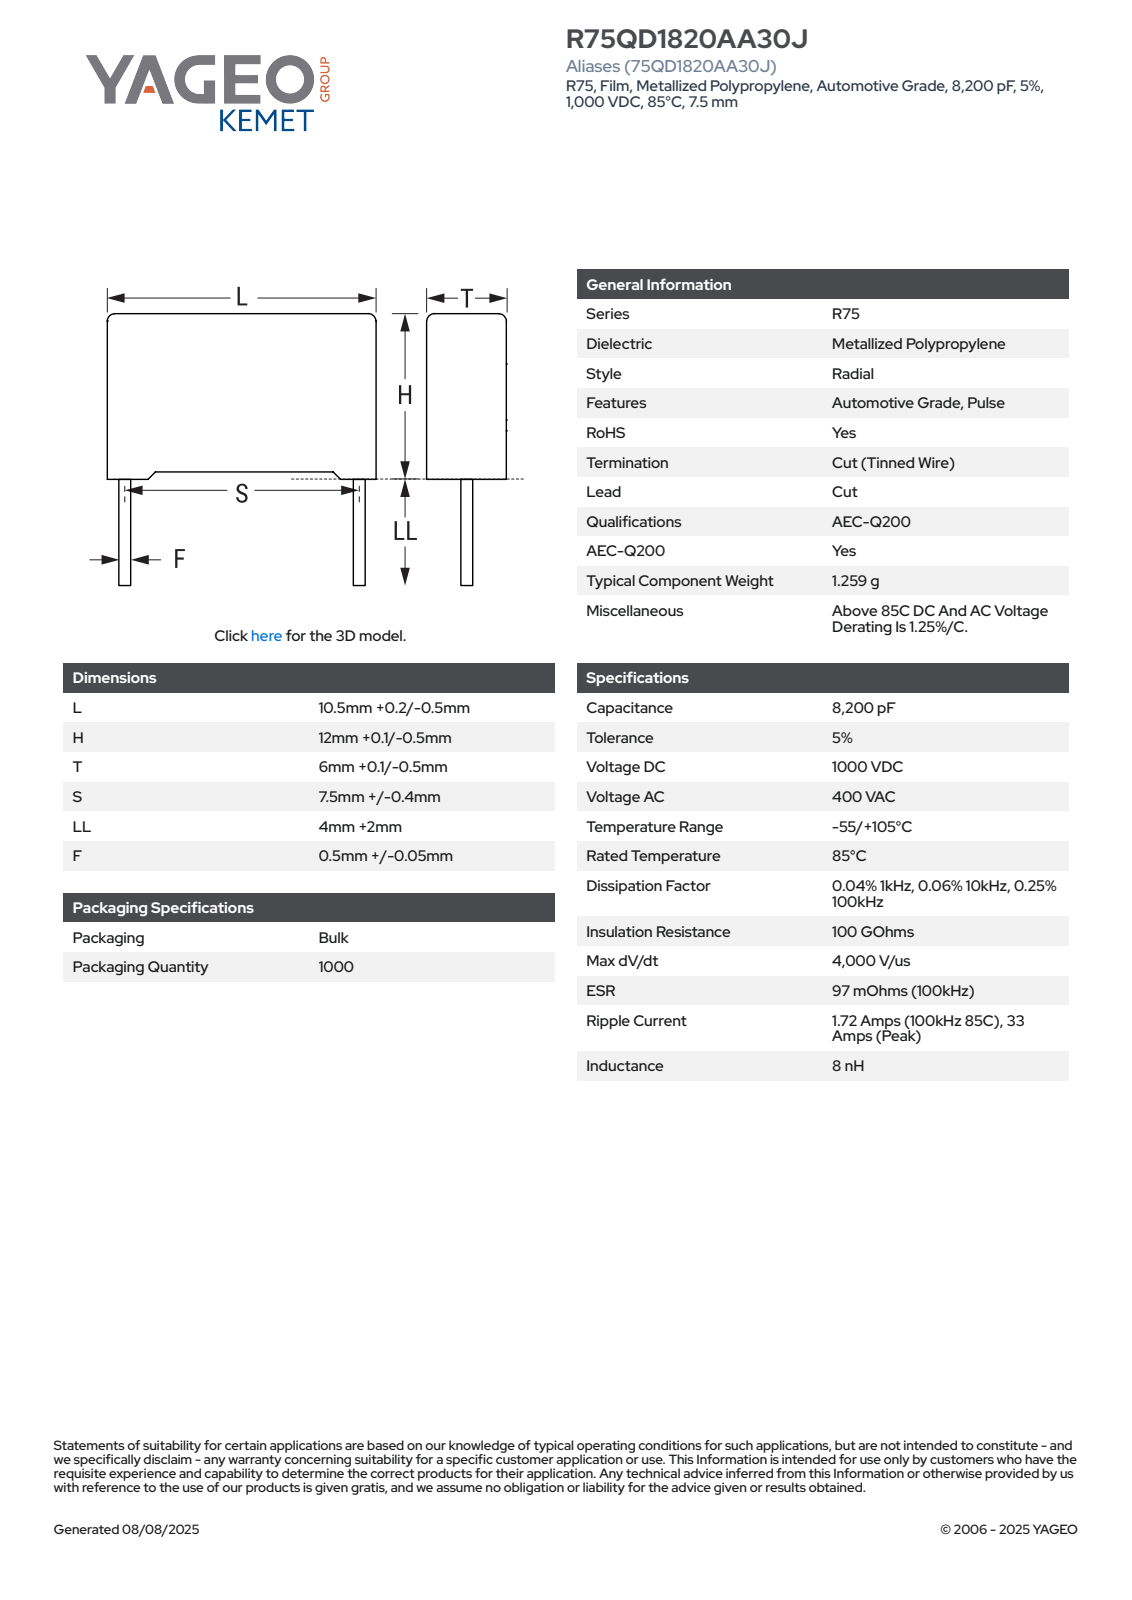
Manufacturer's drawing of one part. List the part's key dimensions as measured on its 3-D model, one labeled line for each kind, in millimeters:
Part name (STEP PRODUCT): CFR_RB2_10.5X12X6_L10.7H12.1T6.1S7.5LL6F0.55
STEP written by: SolidWorks 2021 (AUTOMOTIVE_DESIGN)
Units: millimetres
Bodies: 4 solids, 85 faces (77 planar, 8 cylindrical, 0 other)
Overall size (bounding box): 18.1 × 10.7 × 6.11
Volume: 750 mm³ · Surface area: 578 mm²
Round bosses / shafts (diameter × count): ⌀0.55 ×2
Partial cylindrical surfaces — rounded edges, fillets, slot ends (radius × count): R0.5 ×4
Main face-to-face distances: 6.1, 10.7, 11.35, 0.36, 5.74, 0.75, 12.1, 10.34, 5.38, 9.98
